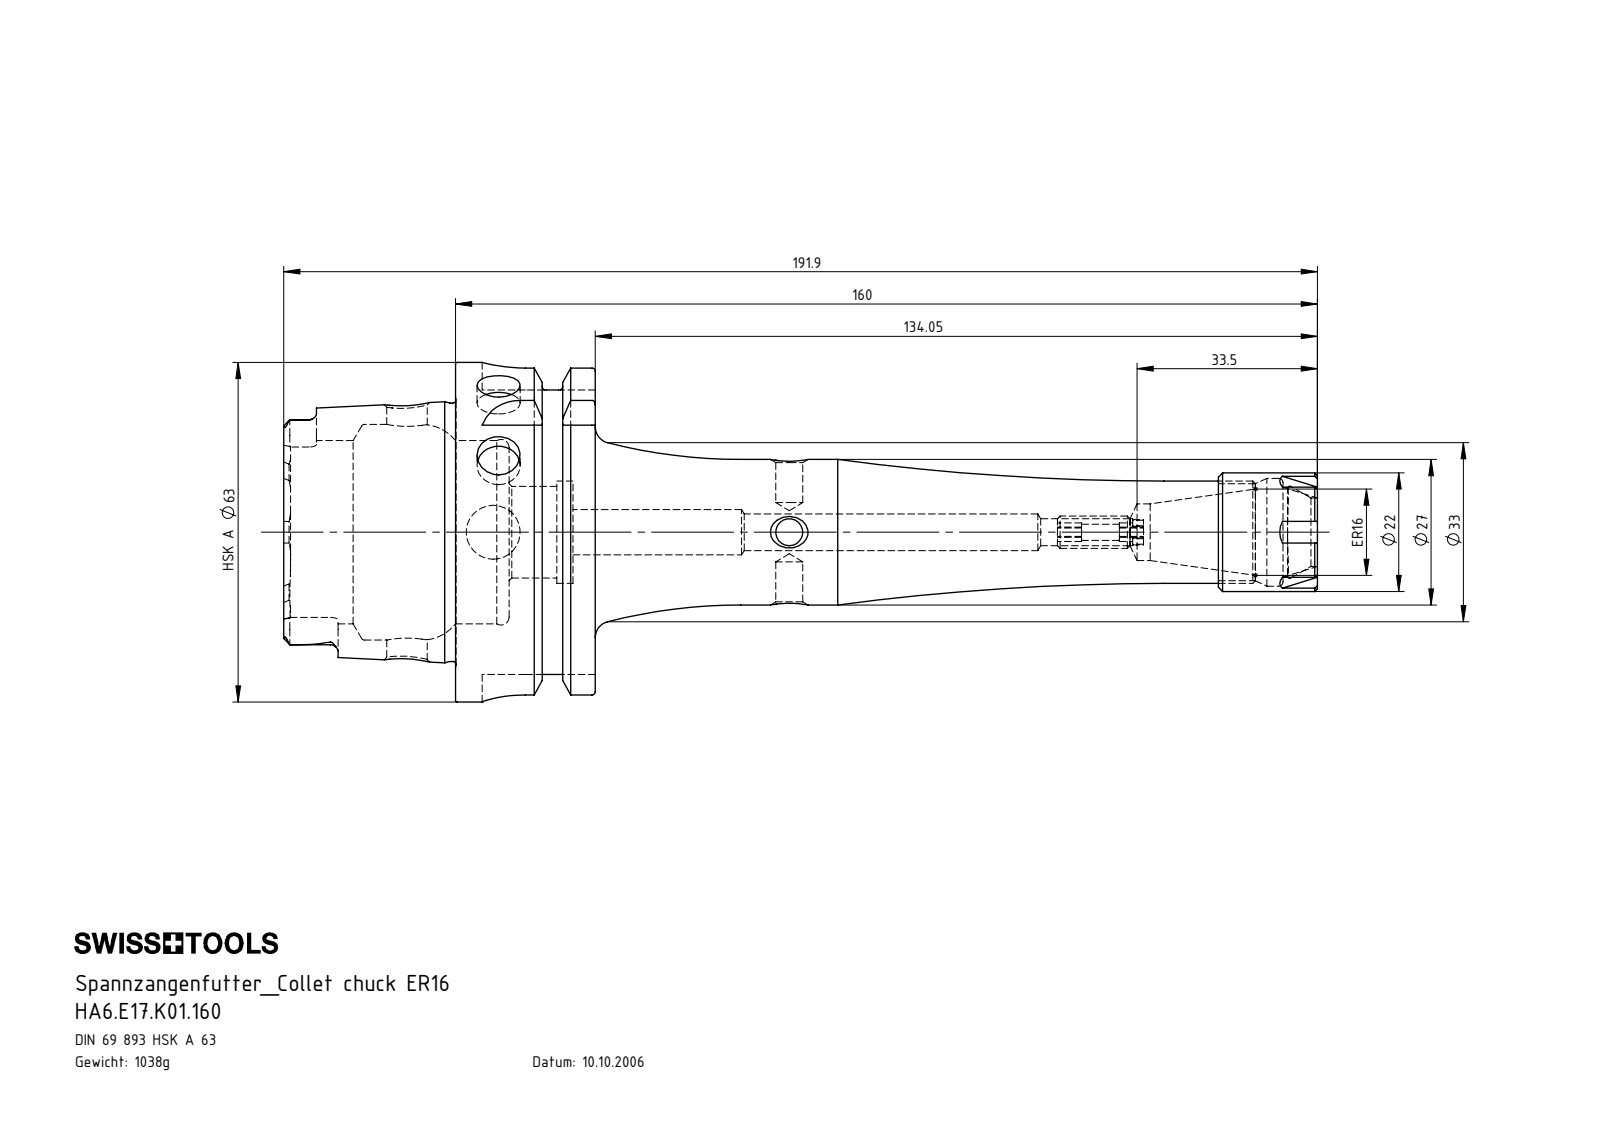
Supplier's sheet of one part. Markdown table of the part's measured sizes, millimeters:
| quantity | value |
| --- | --- |
| part name | HA6.E17.K01.160; ERU-AN2.K01.016_A; E17-ER1.001.018; HA6-E17.K01.160_C_Fertigbearbeitung |
| STEP written by | SolidWorks 2012 (CONFIG_CONTROL_DESIGN) |
| units | millimeters |
| bodies | 3 solids, 311 faces (105 planar, 82 cylindrical, 124 other) |
| overall size | 191.9 × 63 × 63 |
| volume | 132 281 mm³ |
| surface area | 37 642 mm² |
| round holes (diameter × count) | 5 × 3, 8 × 2, 3 × 1, 6.8 × 1, 7.5 × 1, 8.4 × 1, 10 × 1, 10.5 × 1, 12.7 × 1, 17 × 1, 18 × 1, 19 × 1 |
| round bosses / shafts (diameter × count) | 63 × 1, 54.95 × 1, 47.94 × 1, 27 × 1, 22 × 1, 6 × 1 |
| partial cylindrical surfaces (radius × count) | 1.4 × 6, 2.88 × 4, 8 × 4, 7.7 × 2 |
| main face-to-face distances | 25.95, 16, 9.95, 31.9, 41.85, 57.85, 52.8, 21.8, 11.85, 53.7 |
| hole center spacings | 54.95, 70.95 |
